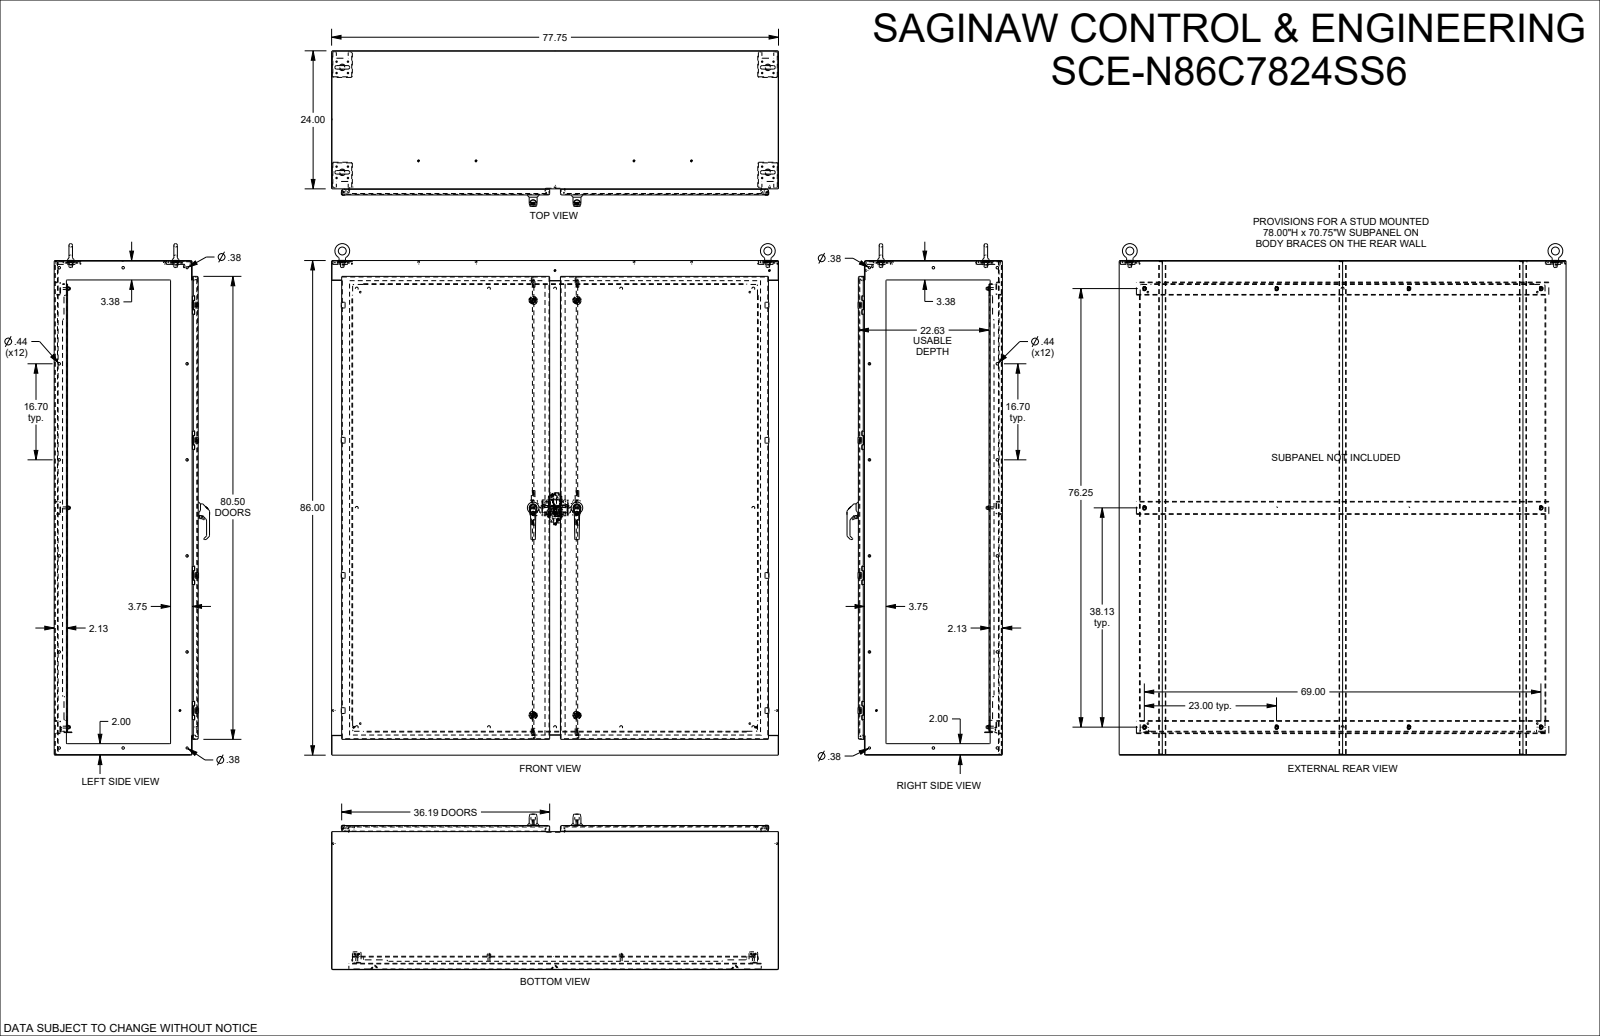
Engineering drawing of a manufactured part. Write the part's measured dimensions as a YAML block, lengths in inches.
part_name: "SCE-N86C7824"
step_written_by: "SolidWorks 2023 (AUTOMOTIVE_DESIGN)"
units: inches
bodies: {solids: 46, faces: 7280, planar: 2956, cylindrical: 2468, other: 1856}
overall_size: [88.945, 77.75, 27.046]
volume: 2237
surface_area: 42522
round_holes:
  - {diameter: 0.25, count: 20}
  - {diameter: 0.375, count: 18}
  - {diameter: 0.205, count: 16}
  - {diameter: 0.244, count: 16}
  - {diameter: 0.437, count: 12}
  - {diameter: 0.04, count: 8}
  - {diameter: 0.17, count: 8}
  - {diameter: 0.218, count: 8}
  - {diameter: 0.256, count: 4}
  - {diameter: 0.343, count: 4}
  - {diameter: 0.344, count: 4}
  - {diameter: 0.36, count: 4}
round_bosses_or_shafts:
  - {diameter: 0.17, count: 24}
  - {diameter: 0.25, count: 20}
  - {diameter: 0.24, count: 16}
  - {diameter: 0.196, count: 10}
  - {diameter: 1.4, count: 4}
  - {diameter: 1.173, count: 4}
  - {diameter: 0.6, count: 4}
  - {diameter: 0.341, count: 4}
partial_cylinders:
  - {radius: 0.03, count: 199}
  - {radius: 0.015, count: 164}
  - {radius: 0.125, count: 100}
  - {radius: 0.02, count: 74}
  - {radius: 0.02, count: 48}
  - {radius: 0.039, count: 42}
  - {radius: 0.04, count: 42}
  - {radius: 0.25, count: 40}
face_to_face_distances: [0.104, 24.954, 25.058, 24.85, 85.896, 23.896, 1.058, 86, 85.792, 23.792]
hole_center_spacings: [23.5, 1.979, 16.7, 27.82, 1.4, 33.4, 40.133, 72.868]
